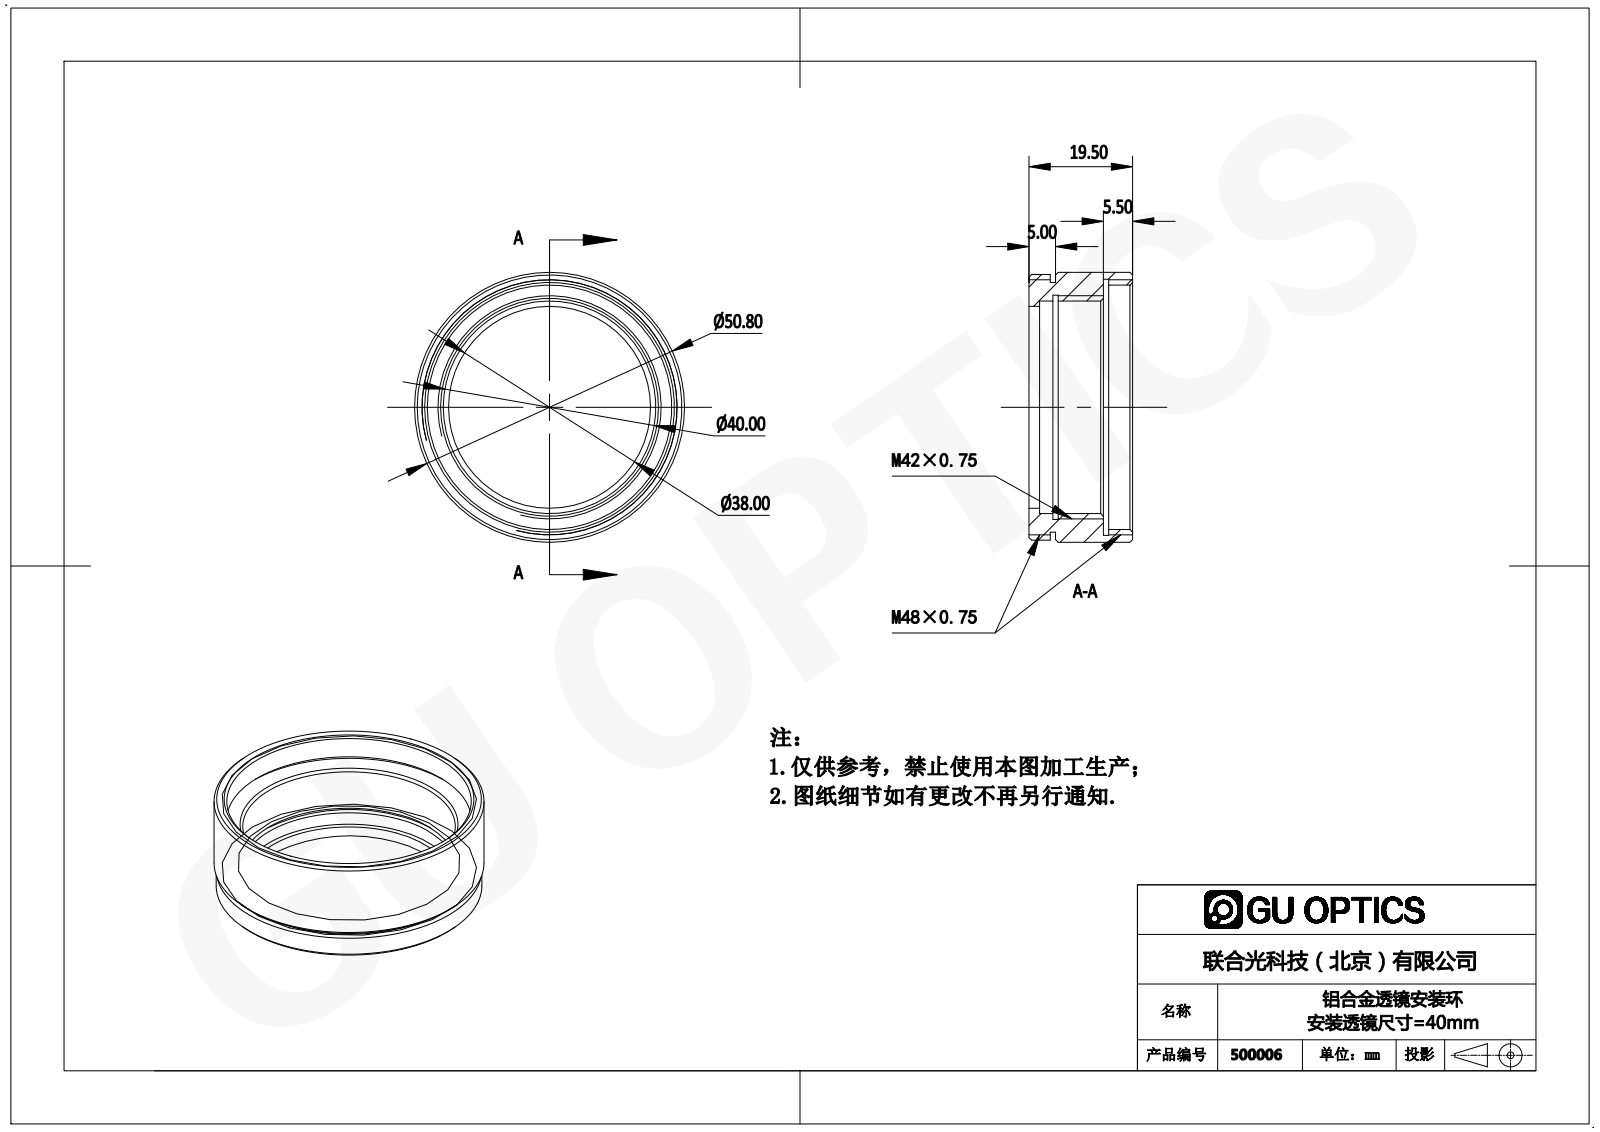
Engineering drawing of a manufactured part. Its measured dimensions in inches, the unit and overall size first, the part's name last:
Units: inches
Overall size (bounding box): 2 × 2 × 0.768
Round holes (diameter × count): ⌀1.496 ×1, ⌀1.575 ×1, ⌀1.661 ×1, ⌀1.811 ×1, ⌀1.898 ×1
Round bosses / shafts (diameter × count): ⌀2 ×1, ⌀1.969 ×1, ⌀1.85 ×1
Main face-to-face distances: 0.551, 0.039, 0.02, 0.394, 0.217, 0.177, 0.591, 0.374, 0.079, 0.157
Volume: 0.738 in³ · Surface area: 12.83 in²
Bodies: 1 solid, 37 faces (9 planar, 18 cylindrical, 10 other)
Part name (STEP PRODUCT): 500006
STEP written by: SolidWorks 2016 (AUTOMOTIVE_DESIGN)
